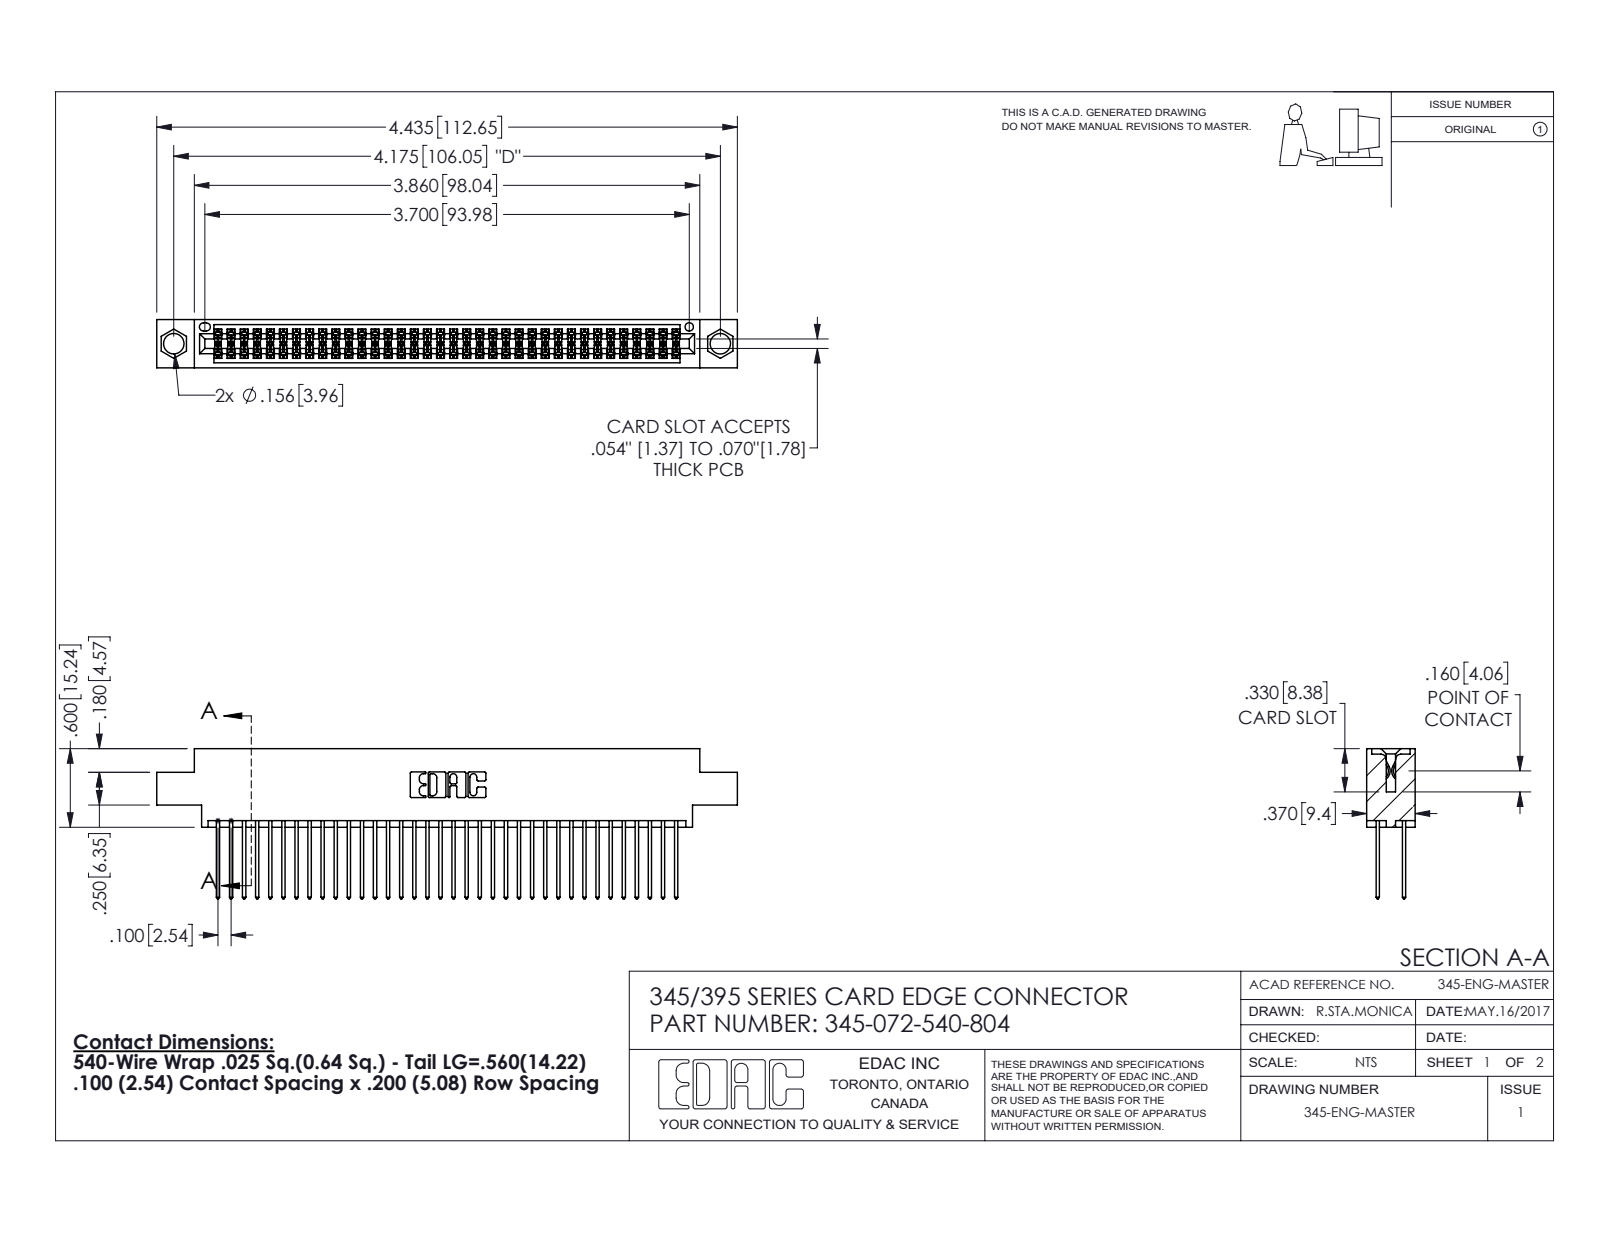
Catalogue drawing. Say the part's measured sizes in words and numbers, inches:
The part is named "345-292-001_345-293-140; 345-072-540-804; 345 Part_0.170 Offset - 0.156 Dia-TI". Its 3-D file was written by "SolidWorks 2020 (CONFIG_CONTROL_DESIGN)". It is 73 solids with 3744 faces: 2474 planar, 1270 cylindrical and 0 other. Overall it measures 4.435 by 1.147 by 0.37 inches. Its volume is 0.668 cubic inches and its surface area 26.84 square inches. Round holes: 2 of diameter 0.156, 1 of diameter 0.064. Partial cylindrical surfaces (rounded edges, fillets, slot ends): 108 of radius 0.006, 72 of radius 0.01, 22 of radius 0.01, 6 of radius 0.007, 6 of radius 0.031, 3 of radius 0.026, 2 of radius 0.014, 2 of radius 0.019. The main face-to-face distances are 0.072, 0.298, 0.2, 0.098, 0.272, 0.025, 0.37, 0.225, 0.175, 0.149. The hole center spacings are 0.27, 3.939, 4.175.
